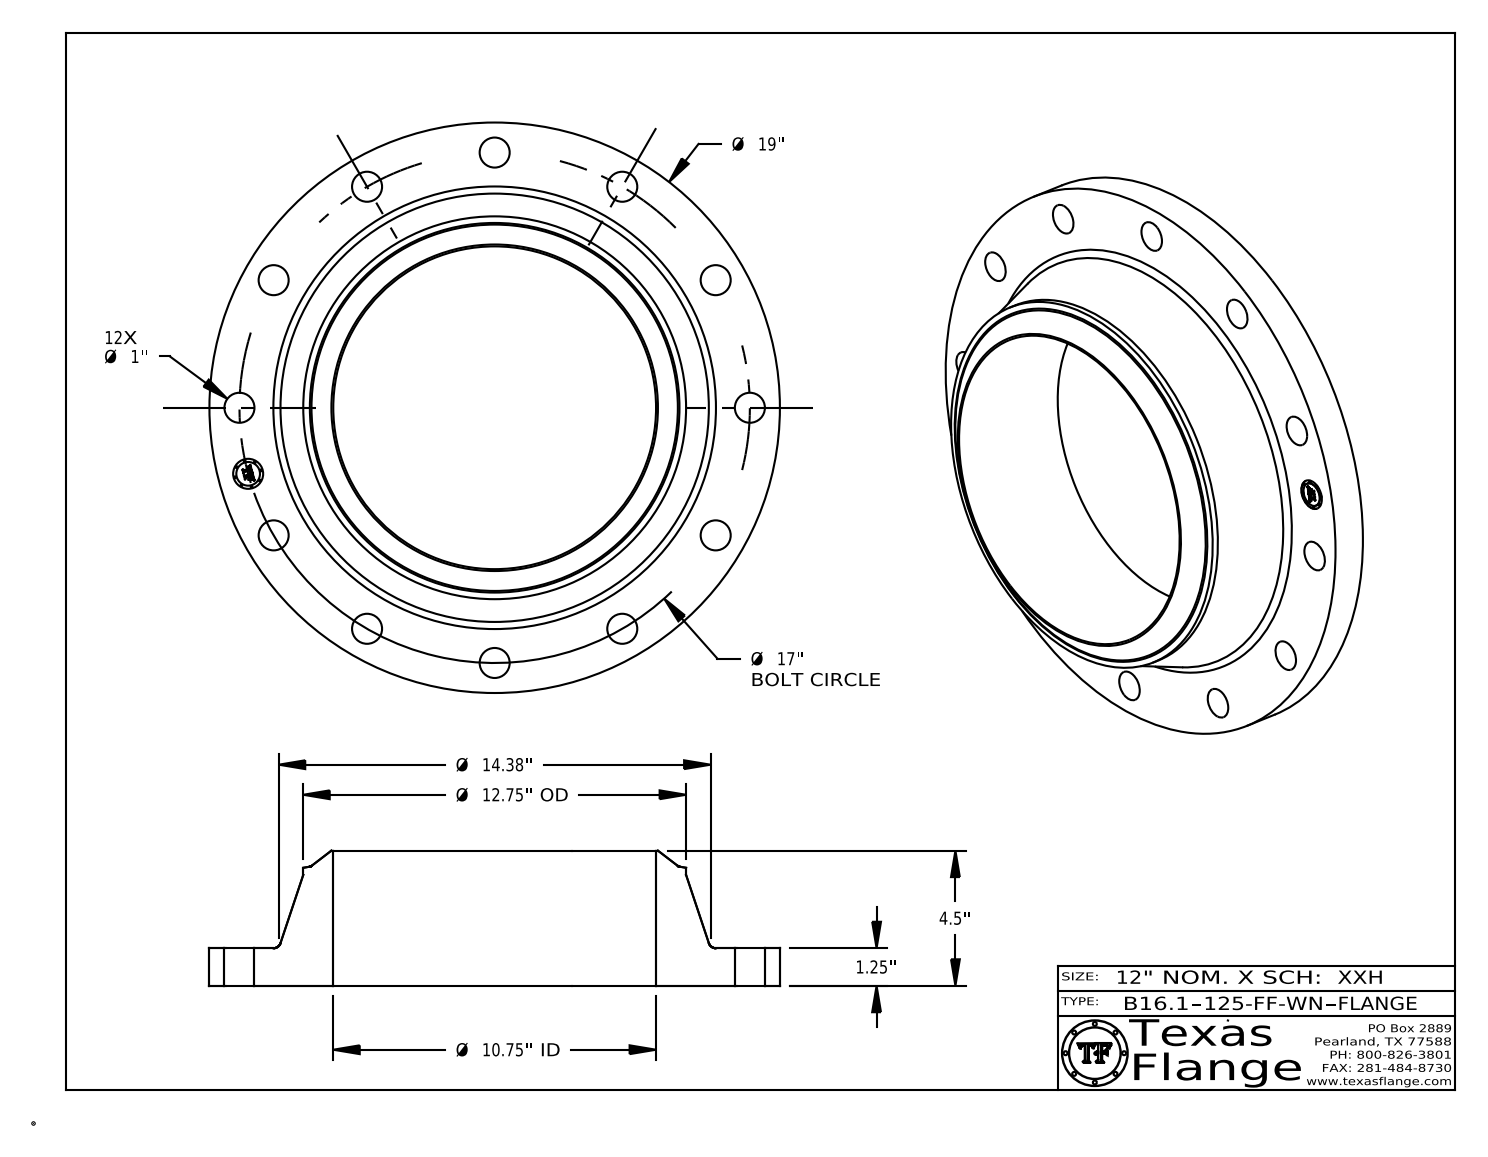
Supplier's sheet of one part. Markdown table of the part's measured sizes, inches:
| quantity | value |
| --- | --- |
| part name | B16.1, Class 125-FF-WN |
| STEP written by | CATIA V5 STEP AP214 (AUTOMOTIVE_DESIGN) |
| units | inches |
| bodies | 1 solid, 428 faces (368 planar, 50 cylindrical, 10 other) |
| overall size | 19 × 19 × 4.5 |
| volume | 378.9 in³ |
| surface area | 729.5 in² |
| round holes (diameter × count) | 1 × 13, 10.75 × 1 |
| round bosses / shafts (diameter × count) | 0.061 × 8, 19 × 1, 12.75 × 1, 0.788 × 1 |
| main face-to-face distances | 1.25, 4.5, 3.25, 0.015, 1.235, 3.265, 0.298, 0.292, 0.054, 0.193 |
| hole center spacings | 8.5, 16.42, 4.4, 12.02, 14.722, 4.4, 12.021, 14.722 |
